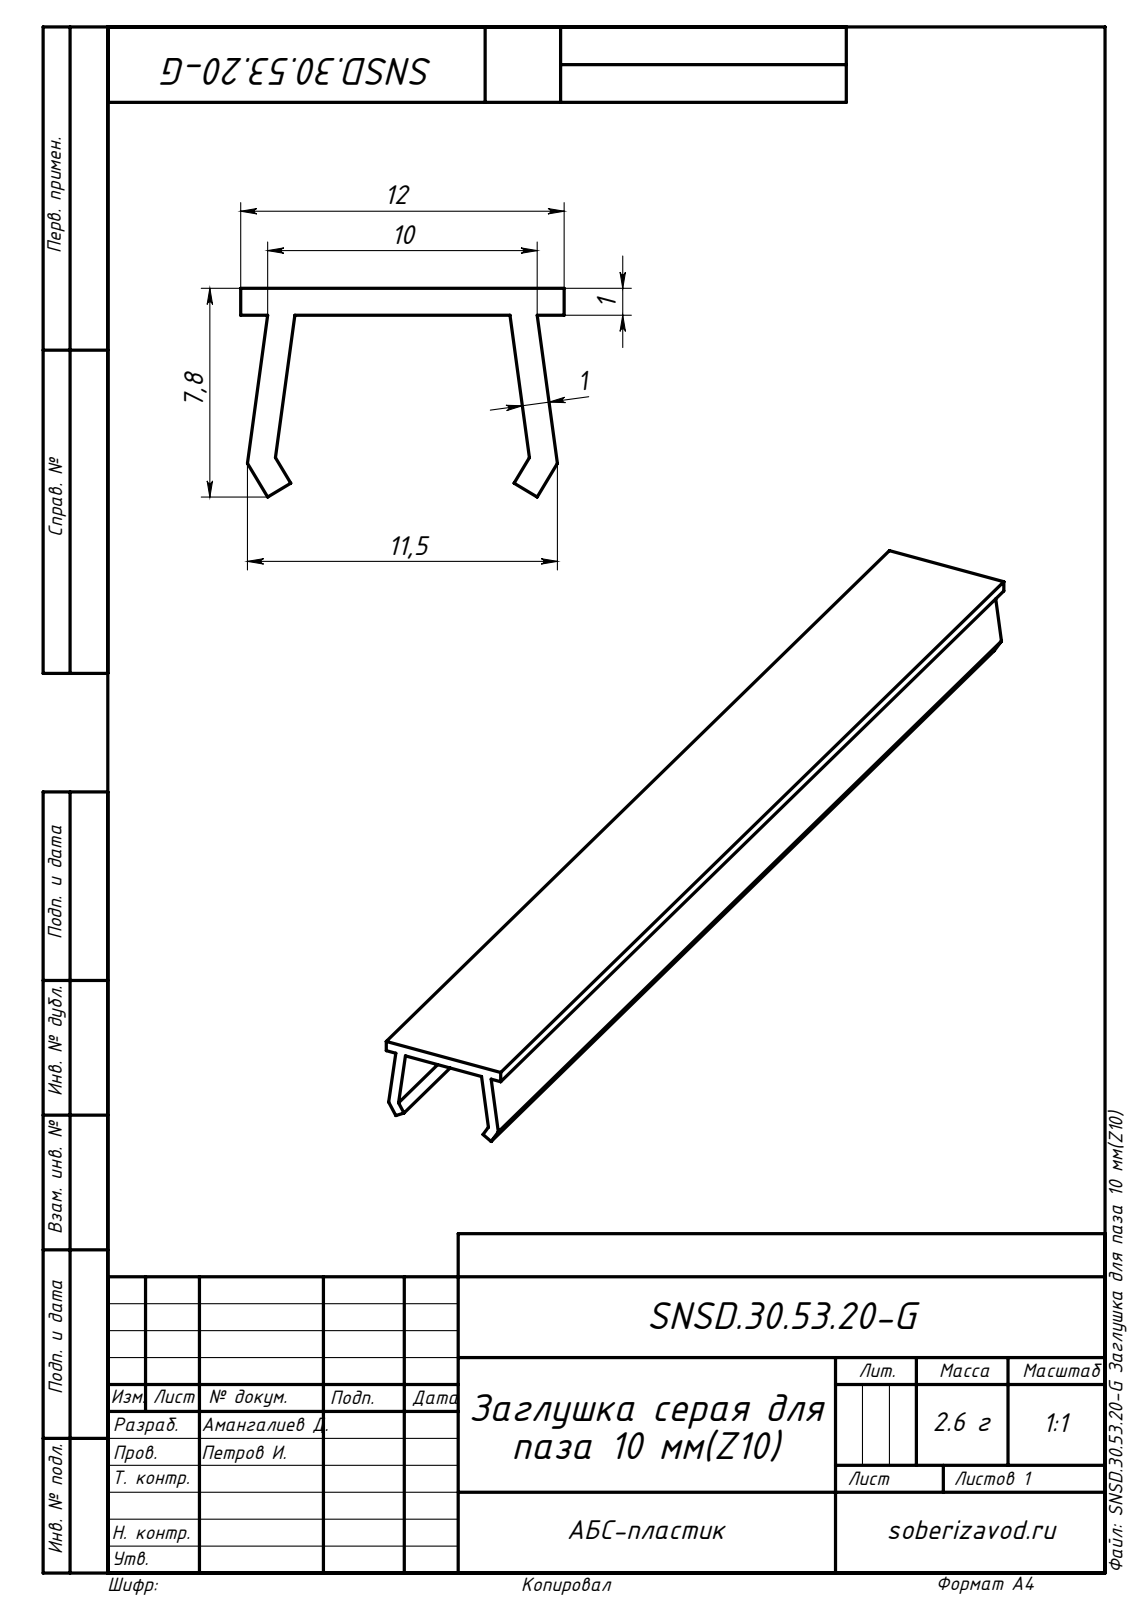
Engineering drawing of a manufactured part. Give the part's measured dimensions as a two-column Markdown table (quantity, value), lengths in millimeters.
| quantity | value |
| --- | --- |
| STEP written by | SolidWorks 2017 (AUTOMOTIVE_DESIGN) |
| units | millimeters |
| bodies | 1 solid, 18 faces (18 planar, 0 cylindrical, 0 other) |
| overall size | 1000 × 12 × 7.75 |
| volume | 25 451 mm³ |
| surface area | 52 934 mm² |
| main face-to-face distances | 1, 12, 1000 |
